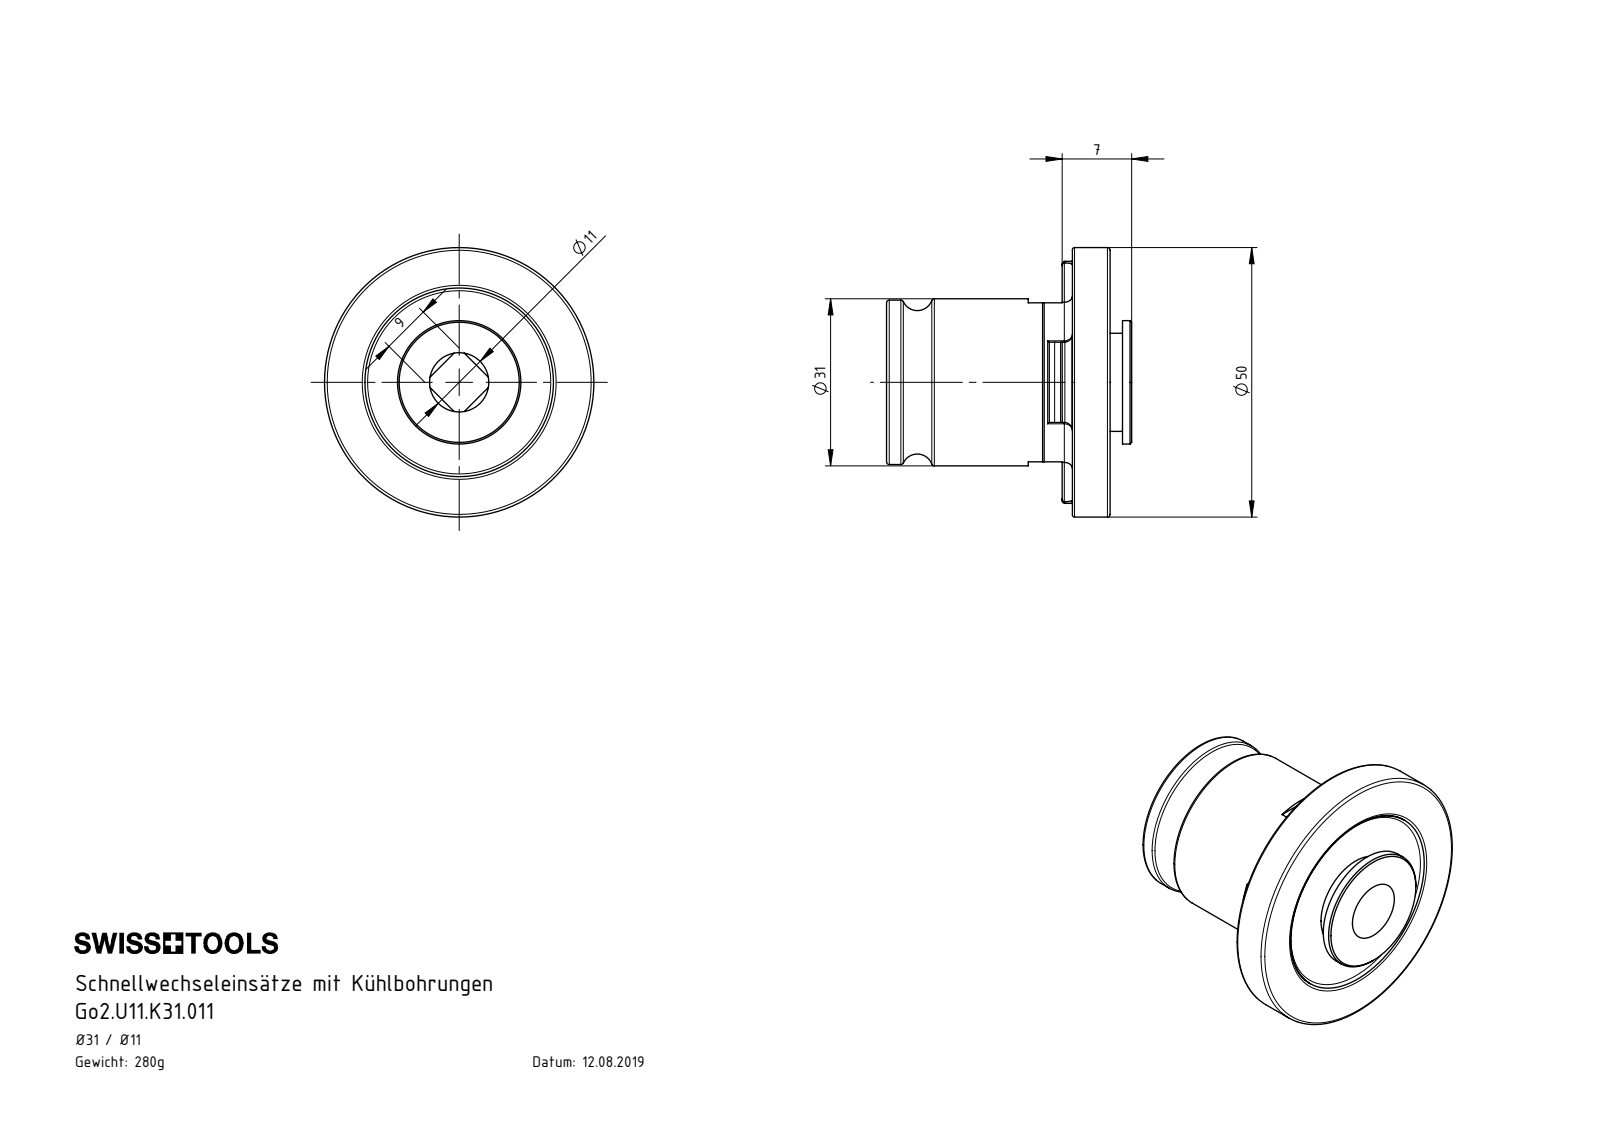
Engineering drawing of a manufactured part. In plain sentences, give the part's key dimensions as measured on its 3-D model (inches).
The part is named "Go2.U11.K31.011". Its 3-D file was written by "SolidWorks 2017 (AUTOMOTIVE_DESIGN)". It is 1 solid with 102 faces: 37 planar, 28 cylindrical and 37 other. Overall it measures 1.969 by 1.969 by 1.791 inches. Its volume is 2.174 cubic inches and its surface area 16.48 square inches. Round holes: 1 of diameter 0.433, 1 of diameter 0.791. Round bosses or shafts: 1 of diameter 1.969, 1 of diameter 1.378, 1 of diameter 1.22, 1 of diameter 1.205, 1 of diameter 1.201, 1 of diameter 0.902, 1 of diameter 0.717. Partial cylindrical surfaces (rounded edges, fillets, slot ends): 5 of radius 0.059, 4 of radius 0.02, 1 of radius 0.787, 1 of radius 0.884. The main face-to-face distances are 0.276, 0.25, 0.026, 1.358, 1.608, 1.634, 1.791, 0.433, 0.183, 0.157.
